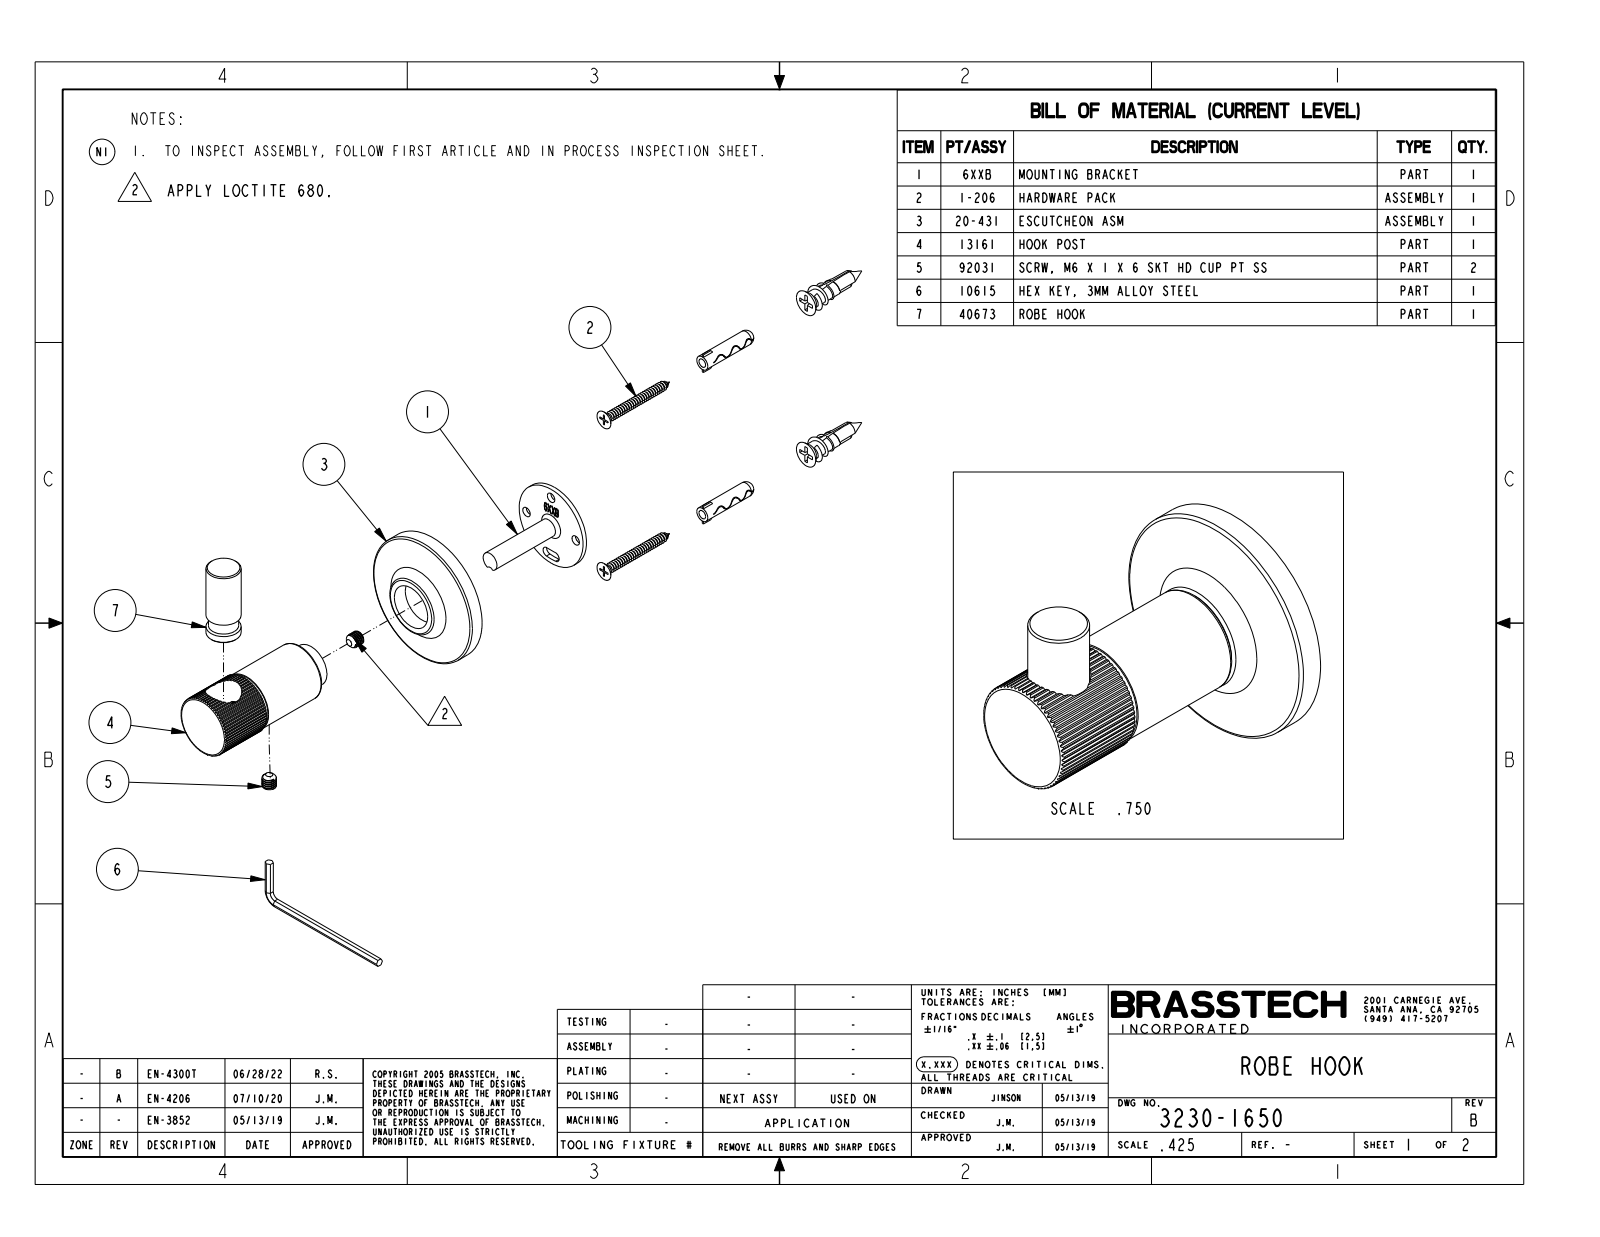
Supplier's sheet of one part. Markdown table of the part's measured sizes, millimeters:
| quantity | value |
| --- | --- |
| part name | 3230-1650 |
| STEP written by | CREO PARAMETRIC BY PTC INC, 2019352 (CONFIG_CONTROL_DESIGN) |
| units | millimeters |
| bodies | 1 solid, 259 faces (159 planar, 86 cylindrical, 14 other) |
| overall size | 69.6 × 57.2 × 57.2 |
| volume | 53 360 mm³ |
| surface area | 12 360 mm² |
| round bosses / shafts (diameter × count) | 57.2 × 1, 25.4 × 1, 24.6 × 1, 21.6 × 1, 14.4 × 1 |
| partial cylindrical surfaces (radius × count) | 13.2 × 1 |
| main face-to-face distances | 20.5, 69.6, 20.5, 12.7, 56.9, 20.4, 13, 56.6, 45.7, 33 |
